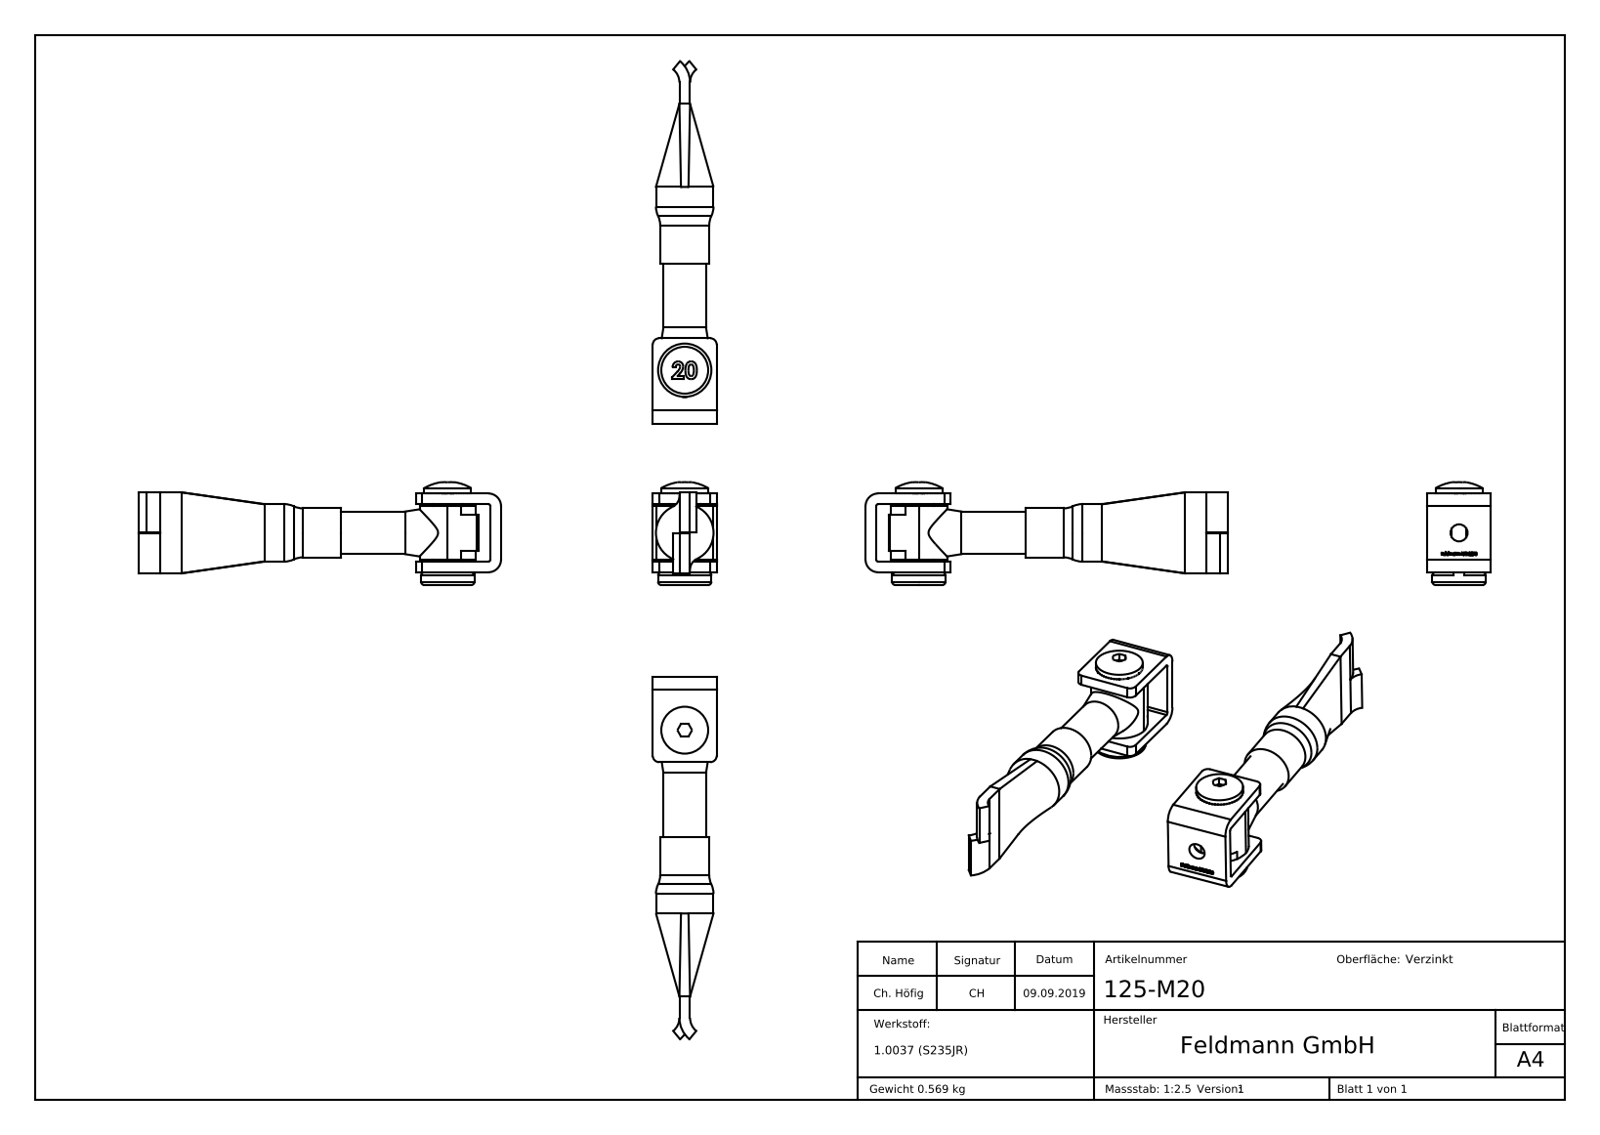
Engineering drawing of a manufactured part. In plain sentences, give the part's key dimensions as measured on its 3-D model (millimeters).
The part is named "125-MXX Teil4_125-M20 Teil4; 125-MXX Teil5_125-M20 Teil5; 125-MXX Teil2_125-M20 Teil2; 125-MXX Teil3_125-M20 Teil3 (+2 more)". Its 3-D file was written by "SolidWorks 2015 (CONFIG_CONTROL_DESIGN)". It is 5 solids with 504 faces: 318 planar, 57 cylindrical and 129 other. Overall it measures 170 by 48.29 by 30 millimeters. Its volume is 72 982 cubic millimeters and its surface area 33 021 square millimeters. Round holes: 1 of diameter 8, 1 of diameter 8.5, 1 of diameter 11, 1 of diameter 14.9, 1 of diameter 15, 1 of diameter 17, 1 of diameter 17.5. Round bosses or shafts: 2 of diameter 22, 1 of diameter 27, 1 of diameter 26.5, 1 of diameter 25, 1 of diameter 23, 1 of diameter 20, 1 of diameter 14.5, 1 of diameter 10. Partial cylindrical surfaces (rounded edges, fillets, slot ends): 2 of radius 1, 2 of radius 3, 2 of radius 6, 2 of radius 7.93, 2 of radius 12.93, 2 of radius 15, 1 of radius 3.1, 1 of radius 10. The main face-to-face distances are 5, 32, 37, 6, 17.5, 27, 12.5, 1, 31, 26.
